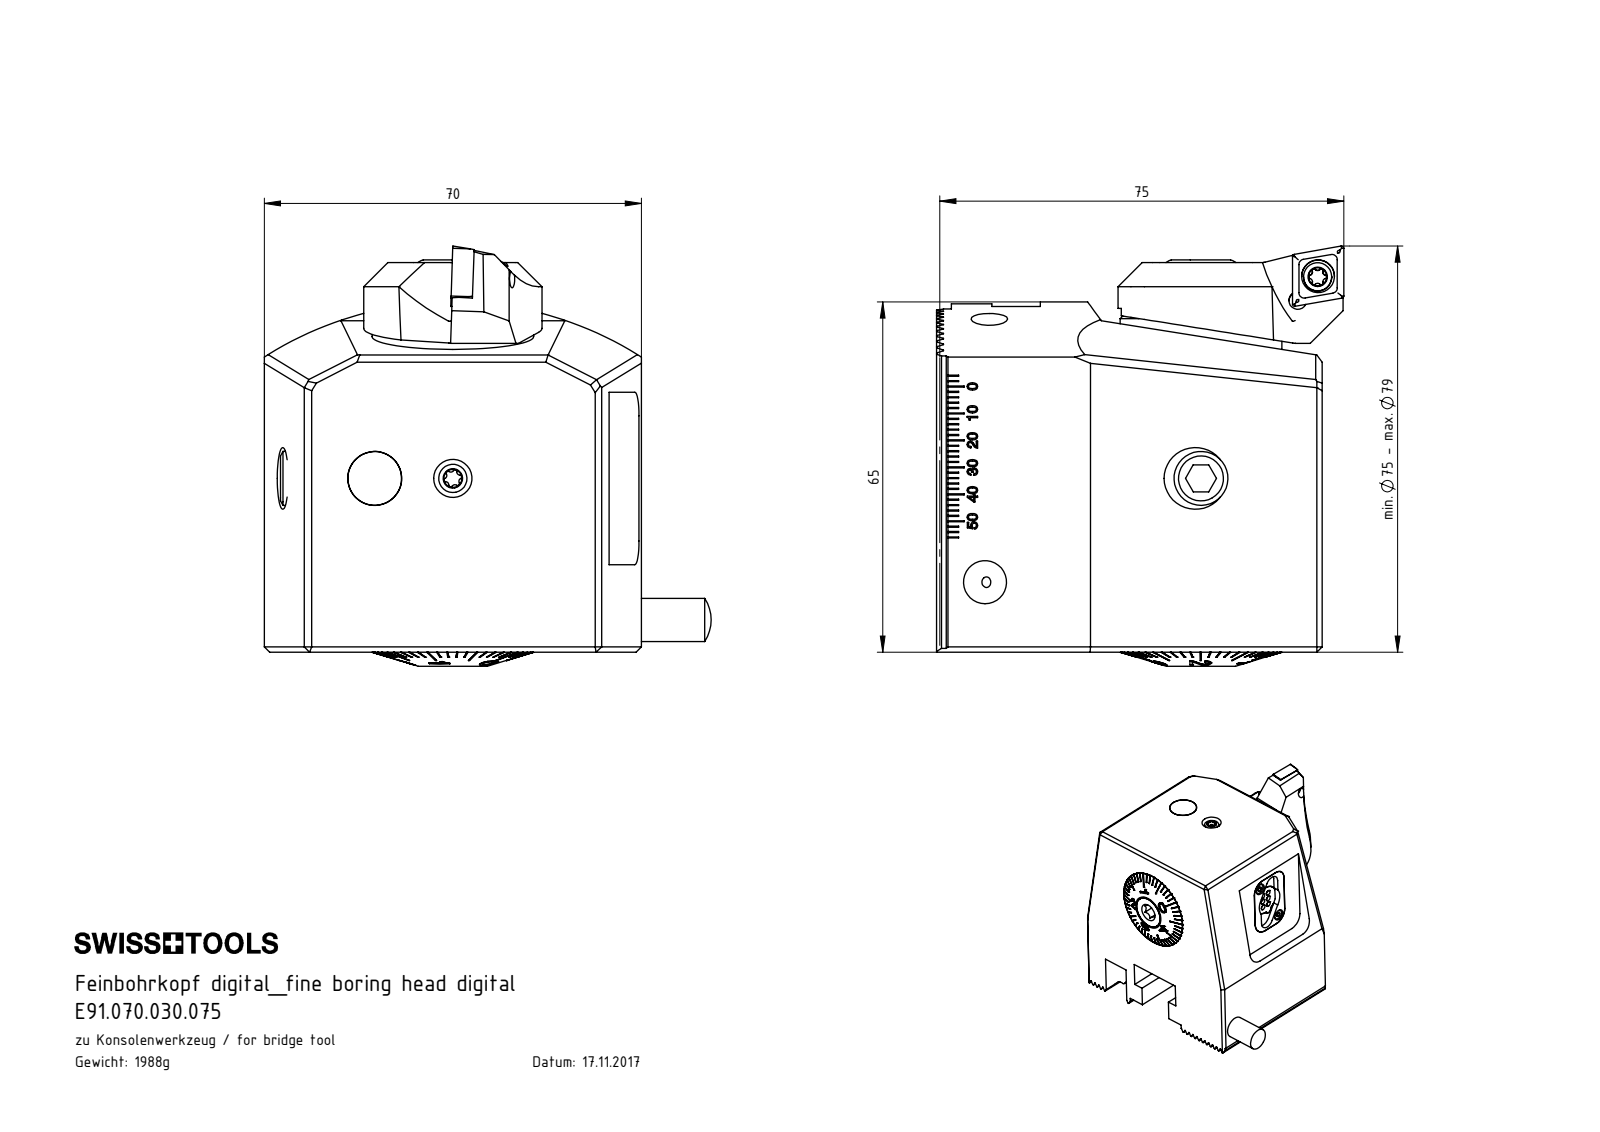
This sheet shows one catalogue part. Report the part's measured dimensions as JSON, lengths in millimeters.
{"part_name": "F72-BG2.014.020_B; Klebstoff D10; A55-BG2.011.016_D; A55-BG3.011.033_A_PreviewCfg (+8 more)", "step_written_by": "SolidWorks 2017 (CONFIG_CONTROL_DESIGN)", "units": "millimeters", "bodies": {"solids": 28, "faces": 1454, "planar": 752, "cylindrical": 273, "other": 429}, "overall_size": [82.95, 77.95, 75.58], "volume_mm3": 254197, "surface_area_mm2": 65176, "round_holes": [[3.3, 4], [4.2, 3], [8, 3], [1.6, 2], [2.2, 2], [8.5, 2], [13, 2], [4.4, 1], [5, 1], [6.1, 1], [6.8, 1], [9.5, 1]], "round_bosses_or_shafts": [[1.9, 6], [10, 2], [5.25, 2], [4, 2], [3.8, 2], [2, 2], [29.98, 1], [29.9, 1]], "partial_cylinders_radius": [[0.14, 22], [0.34, 12], [0.59, 12], [1.2, 8], [1.1, 6], [4.4, 5], [0.5, 4], [4.5, 4]], "face_to_face_distances": [1.73, 5.2, 8.66, 70, 6.93, 3.46, 52.33, 43.3, 24.5, 45.5], "hole_center_spacings": [9.52, 5.72, 5.86, 7, 14.5, 19.04, 39.86, 44.08]}
